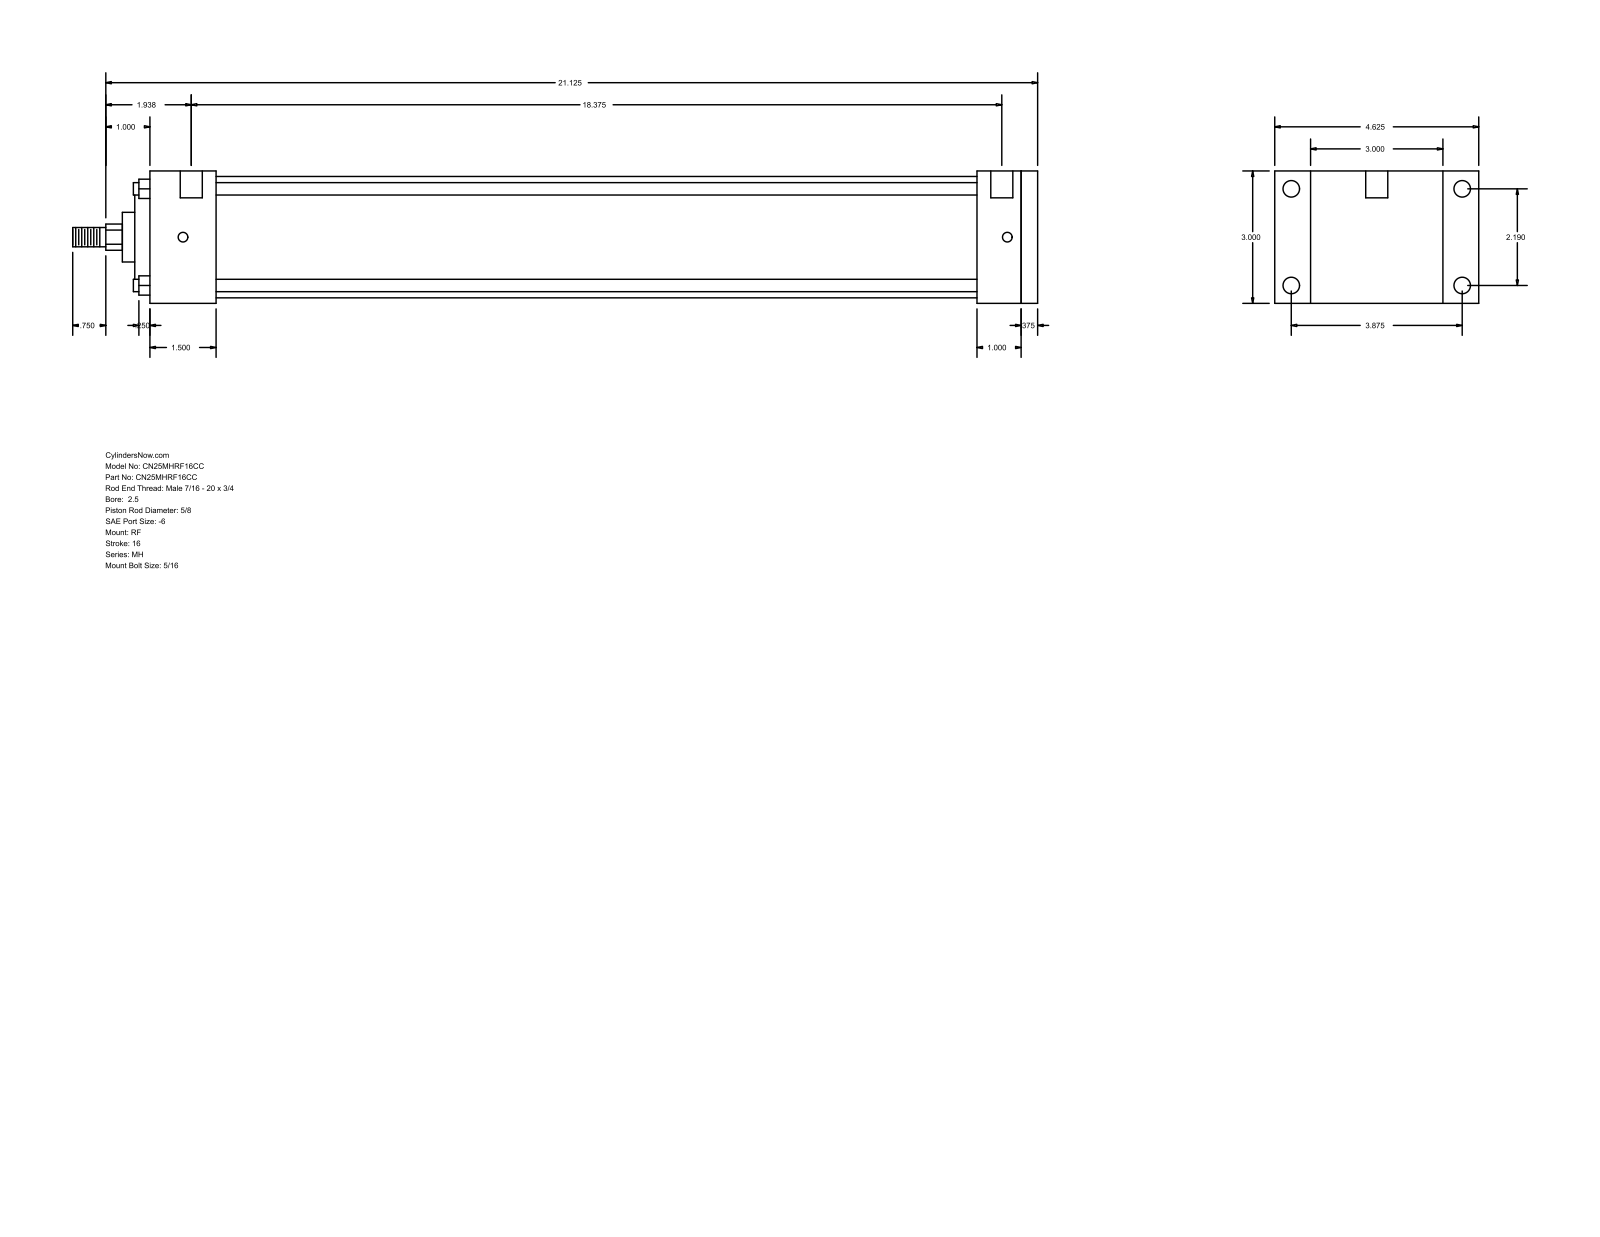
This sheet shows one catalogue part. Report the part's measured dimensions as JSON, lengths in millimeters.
{"part_name": "MH_RF__0250_0.625", "step_written_by": "GSSL Pune (CONFIG_CONTROL_DESIGN)", "units": "millimeters", "bodies": {"solids": 0, "faces": 94, "planar": 65, "cylindrical": 29, "other": 0}, "overall_size": [555.62, 117.47, 76.2], "round_holes": [[5.56, 4], [9.53, 4], [12.7, 2]], "round_bosses_or_shafts": [[7.14, 4], [69.85, 1], [55.55, 1], [28.57, 1], [15.88, 1], [11.11, 1]], "partial_cylinders_radius": [[7.54, 1]], "face_to_face_distances": [76.2, 9.53, 511.18, 501.65, 25.4, 34.93, 38.1, 476.25, 438.15, 463.55], "hole_center_spacings": [55.62, 98.42, 113.05, 474.66, 3.17, 4.76, 466.73, 469.9]}
